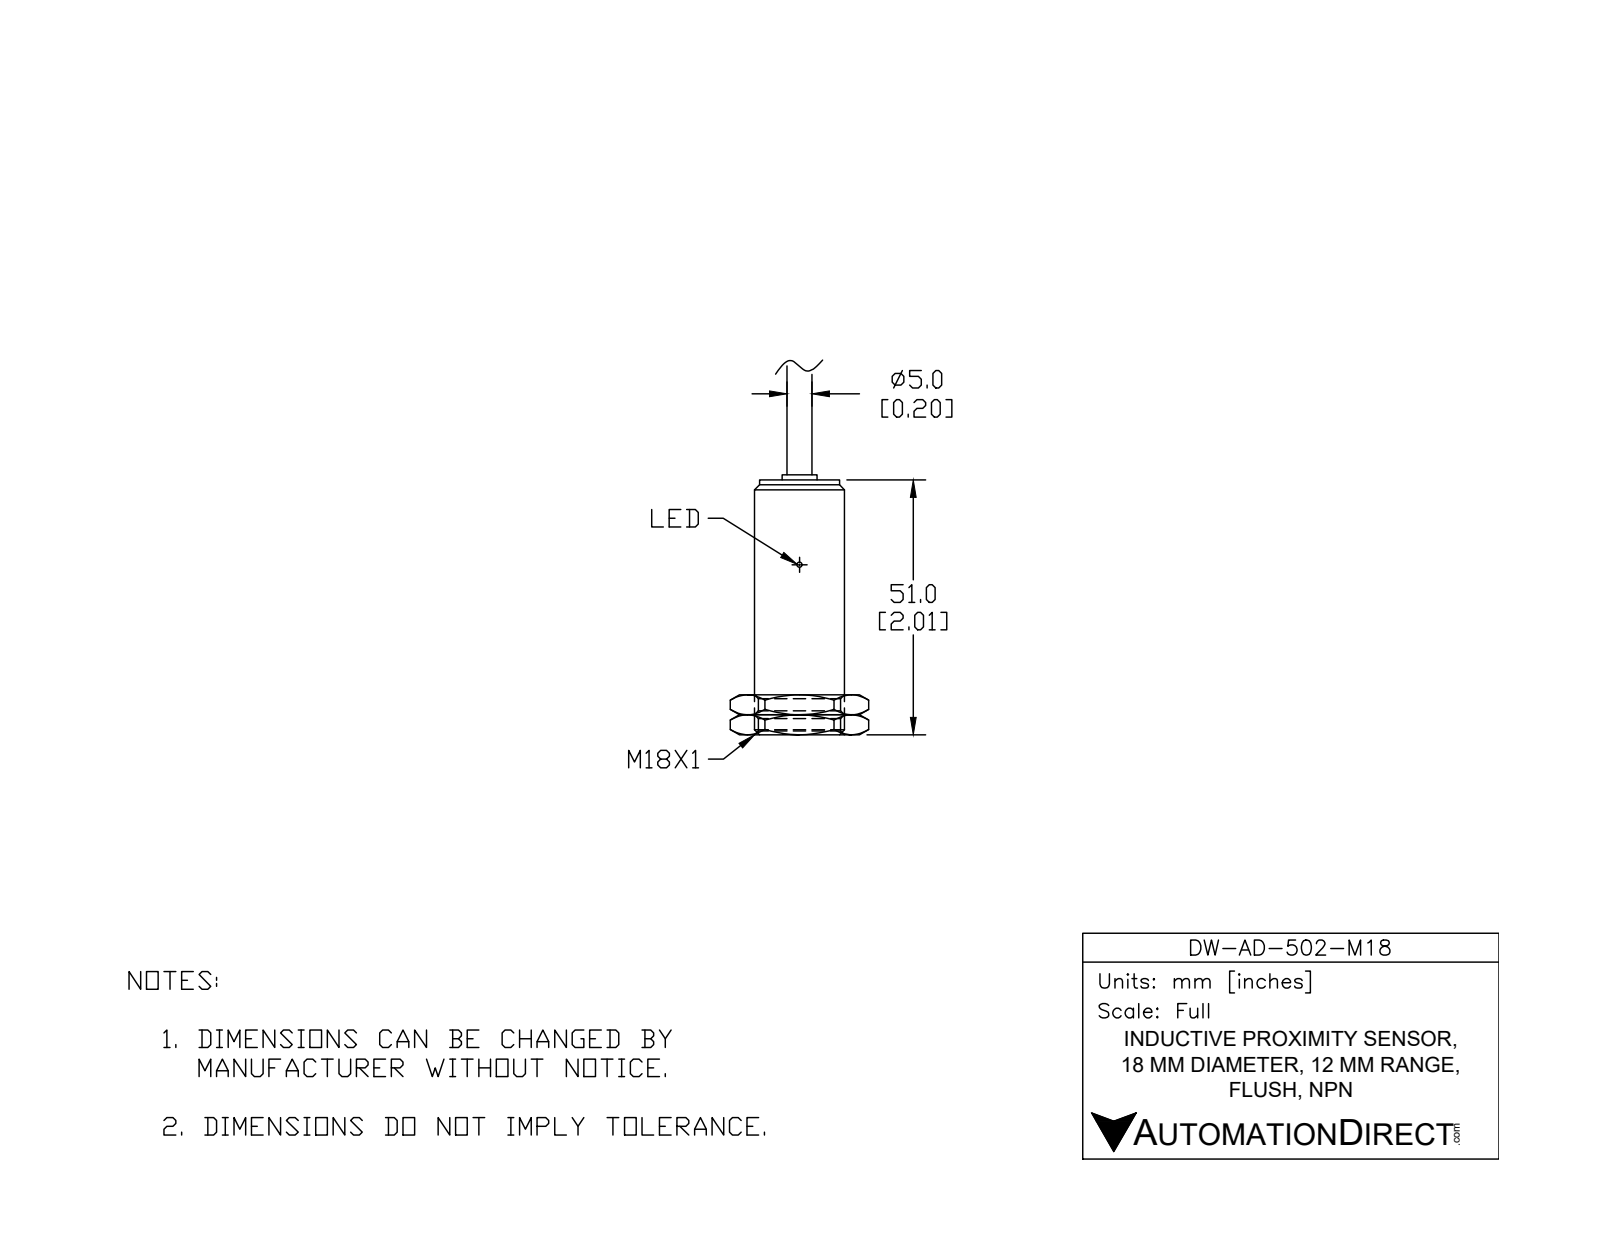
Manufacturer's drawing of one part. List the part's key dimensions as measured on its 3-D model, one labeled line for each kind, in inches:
Part name (STEP PRODUCT): DW-AD-50x-M18
STEP written by: SolidWorks 2017 (AUTOMOTIVE_DESIGN)
Units: inches
Bodies: 2 solids, 36 faces (18 planar, 6 cylindrical, 12 other)
Overall size (bounding box): 3.016 × 0.709 × 0.709
Volume: 0.826 in³ · Surface area: 5.994 in²
Round bosses / shafts (diameter × count): ⌀0.709 ×1, ⌀0.646 ×1, ⌀0.413 ×1, ⌀0.268 ×1, ⌀0.197 ×1, ⌀0.118 ×1
Main face-to-face distances: 2, 0.031, 2.079, 0.079, 2.031, 0.047, 1.882, 0.118, 0.15, 0.197
